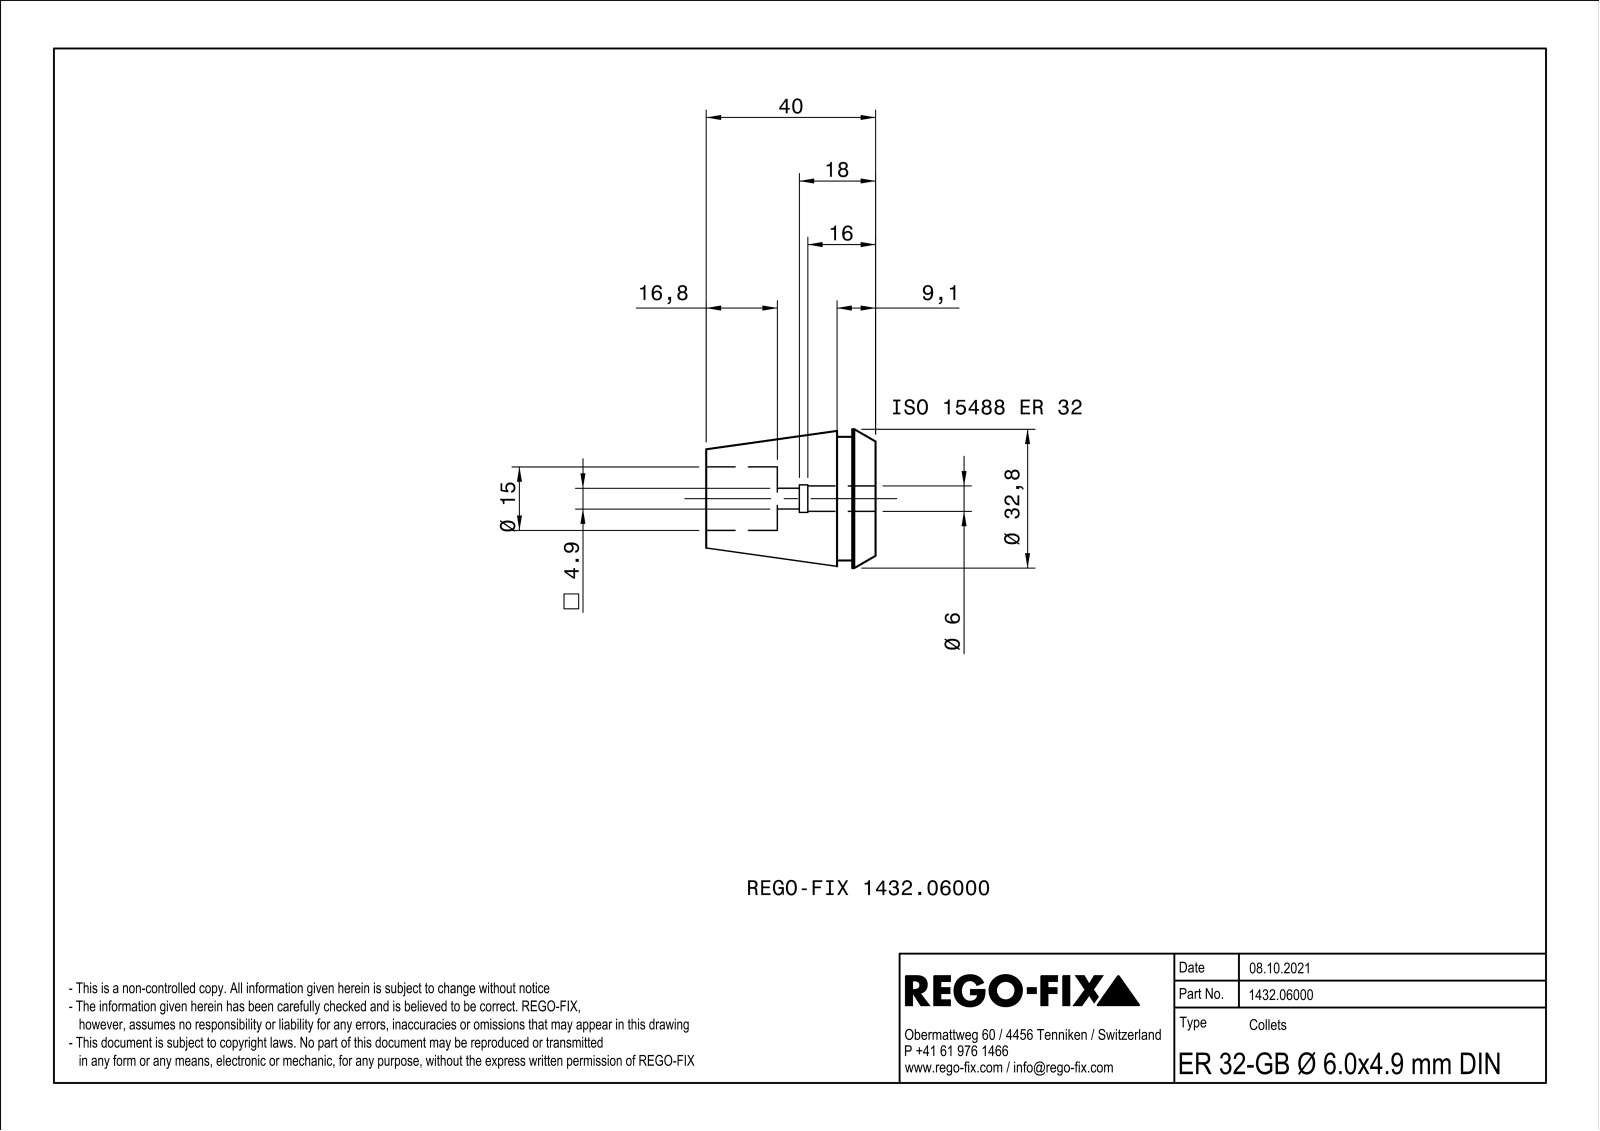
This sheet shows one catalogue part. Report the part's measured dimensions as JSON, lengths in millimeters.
{"part_name": "NOCUT", "step_written_by": "SIEMENS PLM Software Solid Edge ST10 (AUTOMOTIVE_DESIGN)", "units": "millimeters", "bodies": {"solids": 1, "faces": 160, "planar": 76, "cylindrical": 40, "other": 44}, "overall_size": [40, 32.79, 32.79], "volume_mm3": 19358, "surface_area_mm2": 10793, "round_holes": [[6, 1], [15, 1]], "round_bosses_or_shafts": [[32.8, 1], [29.2, 1]], "partial_cylinders_radius": [[2.8, 1], [3.15, 1], [3.25, 1]], "face_to_face_distances": [0.8, 40, 5.5, 34.5, 9.1, 3.6, 30.9, 23.2, 17.7, 14.1]}
